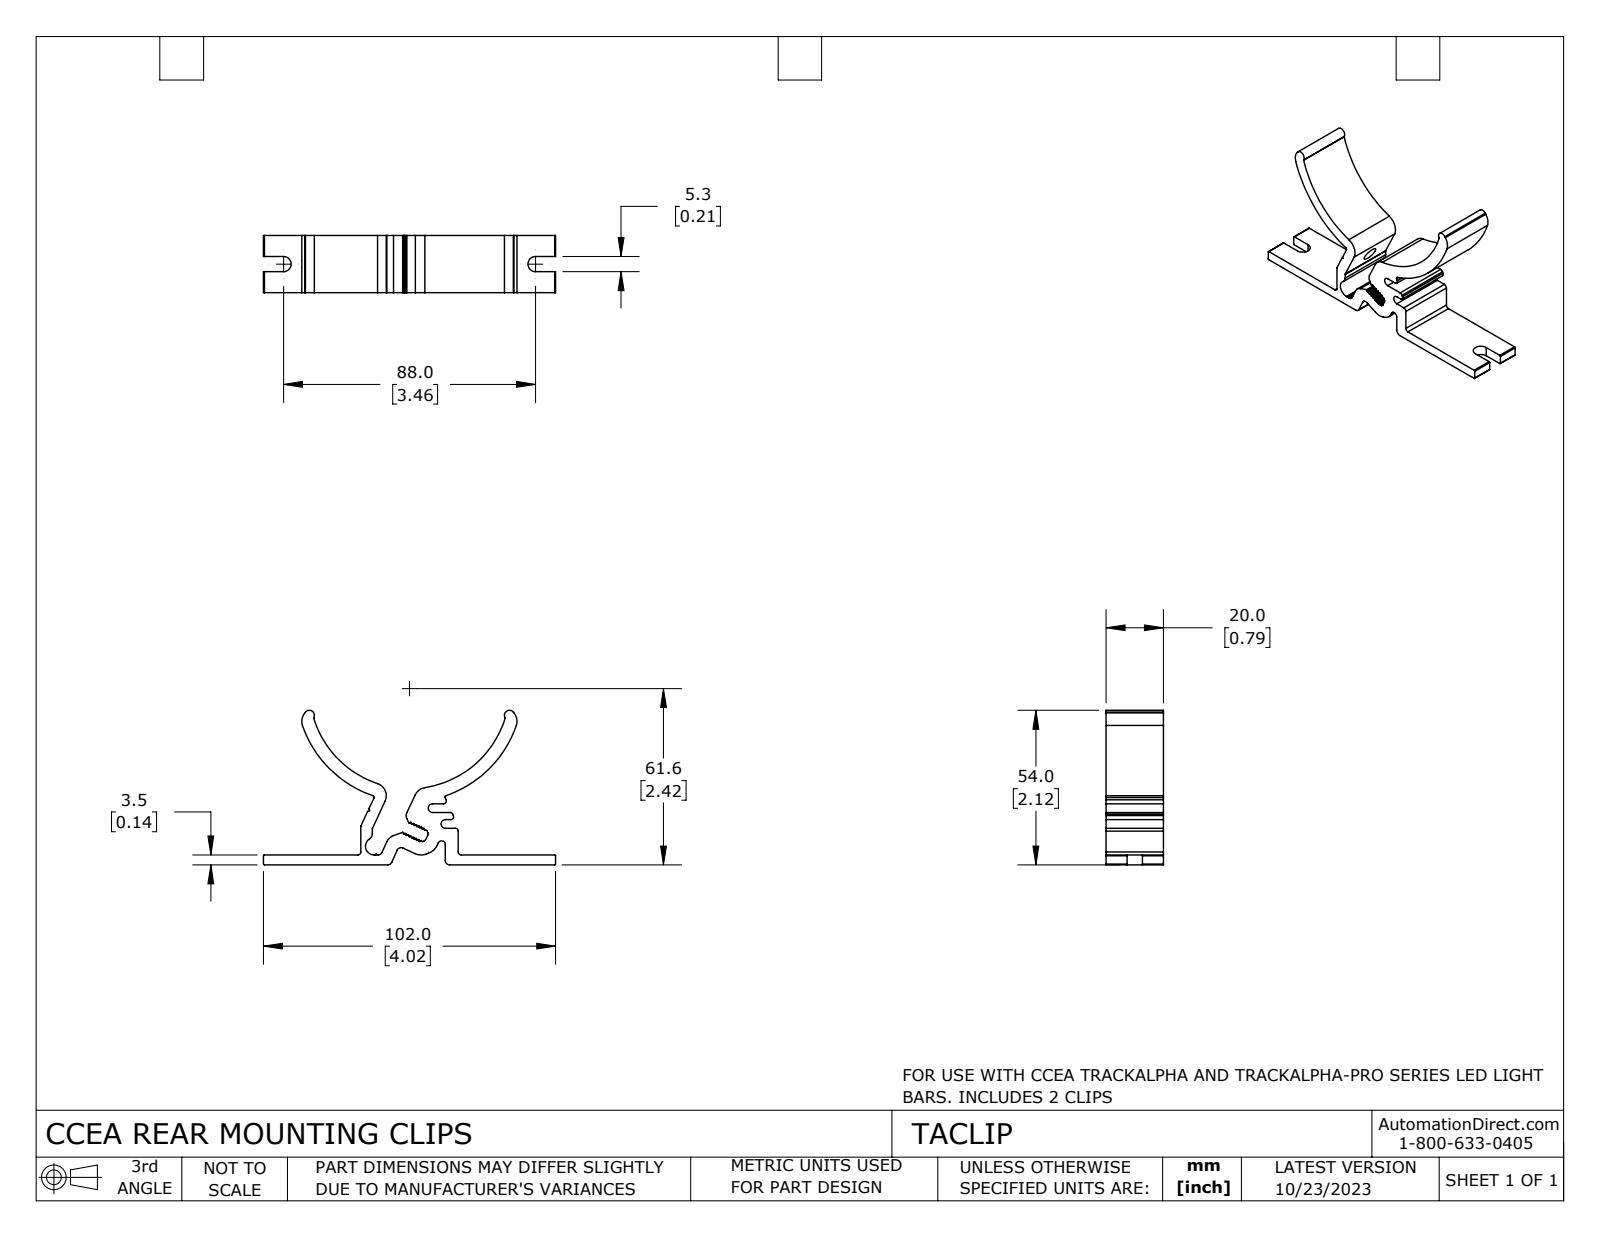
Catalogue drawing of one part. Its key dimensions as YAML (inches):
part_name: "TACLIP"
step_written_by: "SolidWorks 2023 (CONFIG_CONTROL_DESIGN)"
units: inches
bodies: {solids: 1, faces: 169, planar: 87, cylindrical: 82, other: 0}
overall_size: [4.016, 2.125, 0.787]
volume: 1.243
surface_area: 18.79
round_holes:
  - {diameter: 0.209, count: 1}
partial_cylinders:
  - {radius: 0.01, count: 15}
  - {radius: 0.039, count: 8}
  - {radius: 0.012, count: 7}
  - {radius: 0.059, count: 6}
  - {radius: 0.02, count: 5}
  - {radius: 0.177, count: 4}
  - {radius: 0.069, count: 2}
  - {radius: 0.098, count: 2}
face_to_face_distances: [0.138, 0.787, 0.177, 1.339, 0.157, 0.721, 0.583, 0.118, 1.161, 0.217]
